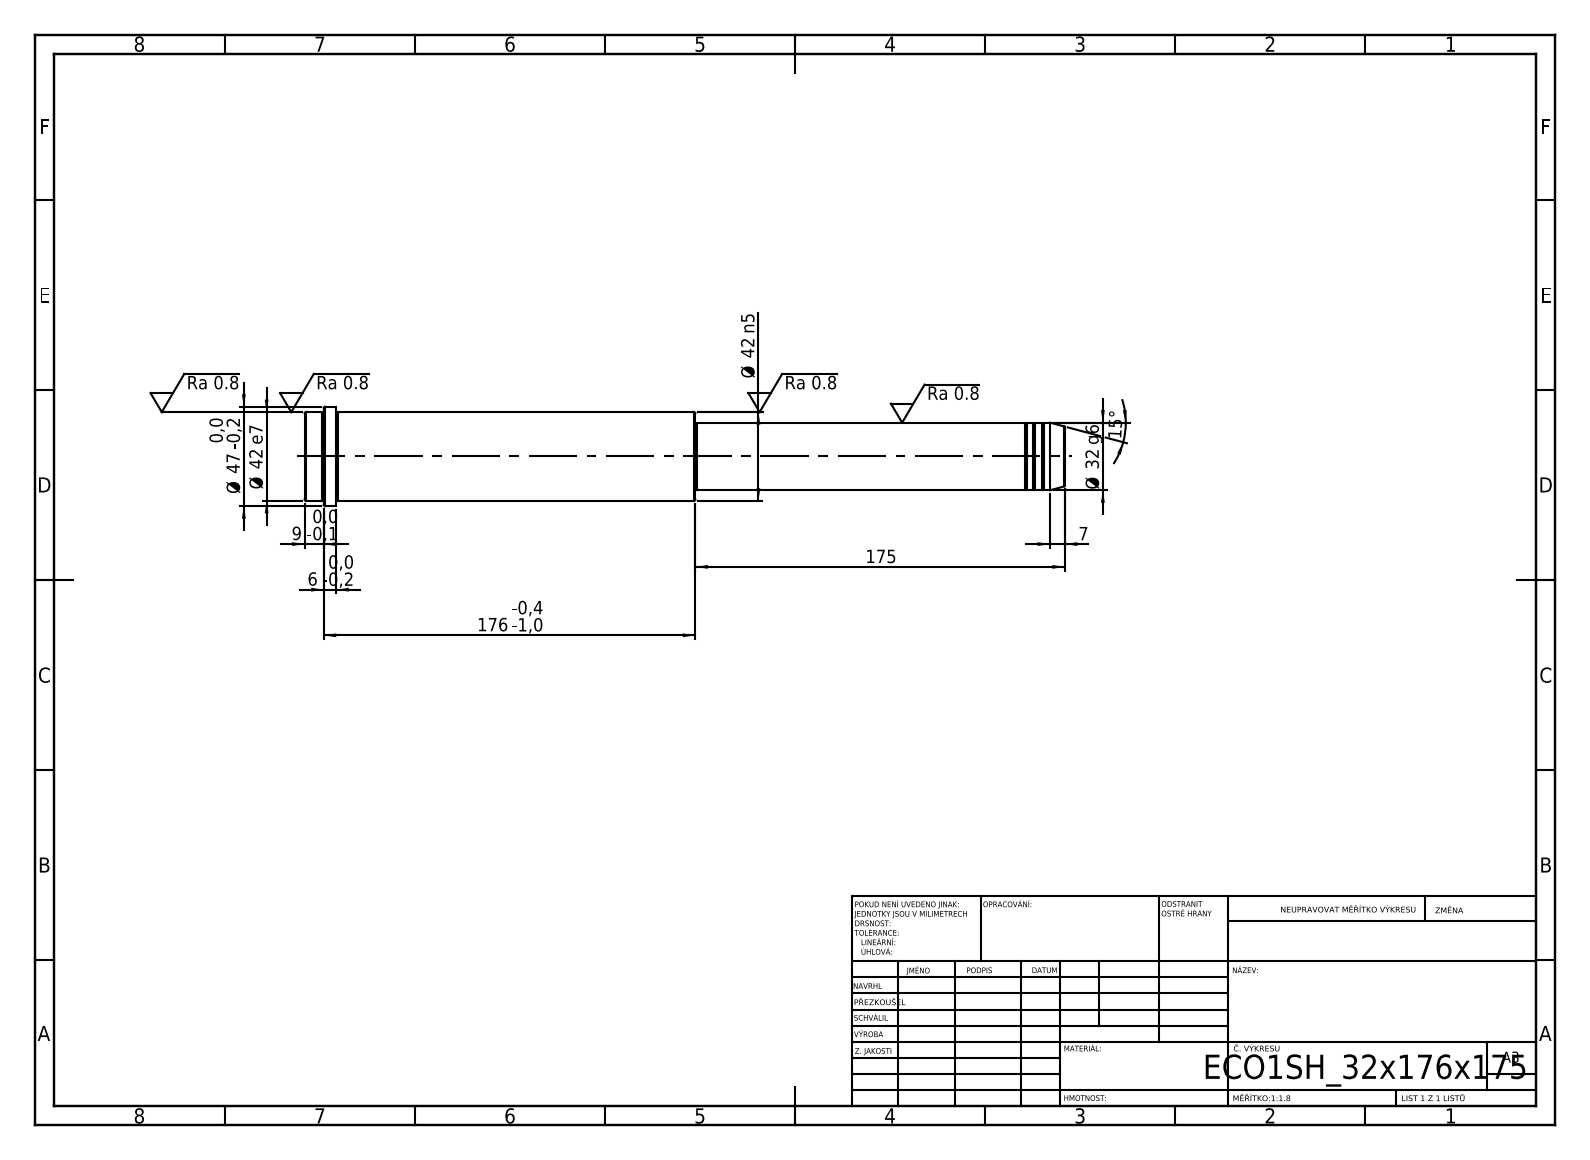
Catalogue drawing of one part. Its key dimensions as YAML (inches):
step_written_by: "SolidWorks 2019 (CONFIG_CONTROL_DESIGN)"
units: inches
bodies: {solids: 1, faces: 52, planar: 6, cylindrical: 16, other: 30}
overall_size: [14.173, 1.85, 1.85]
volume: 24.3
surface_area: 70.75
round_bosses_or_shafts:
  - {diameter: 1.85, count: 1}
  - {diameter: 1.654, count: 1}
  - {diameter: 1.26, count: 1}
  - {diameter: 1.22, count: 1}
face_to_face_distances: [14.173, 6.89, 7.283, 13.583, 6.693, 0.591, 13.819, 6.929, 0.236, 0.354]
